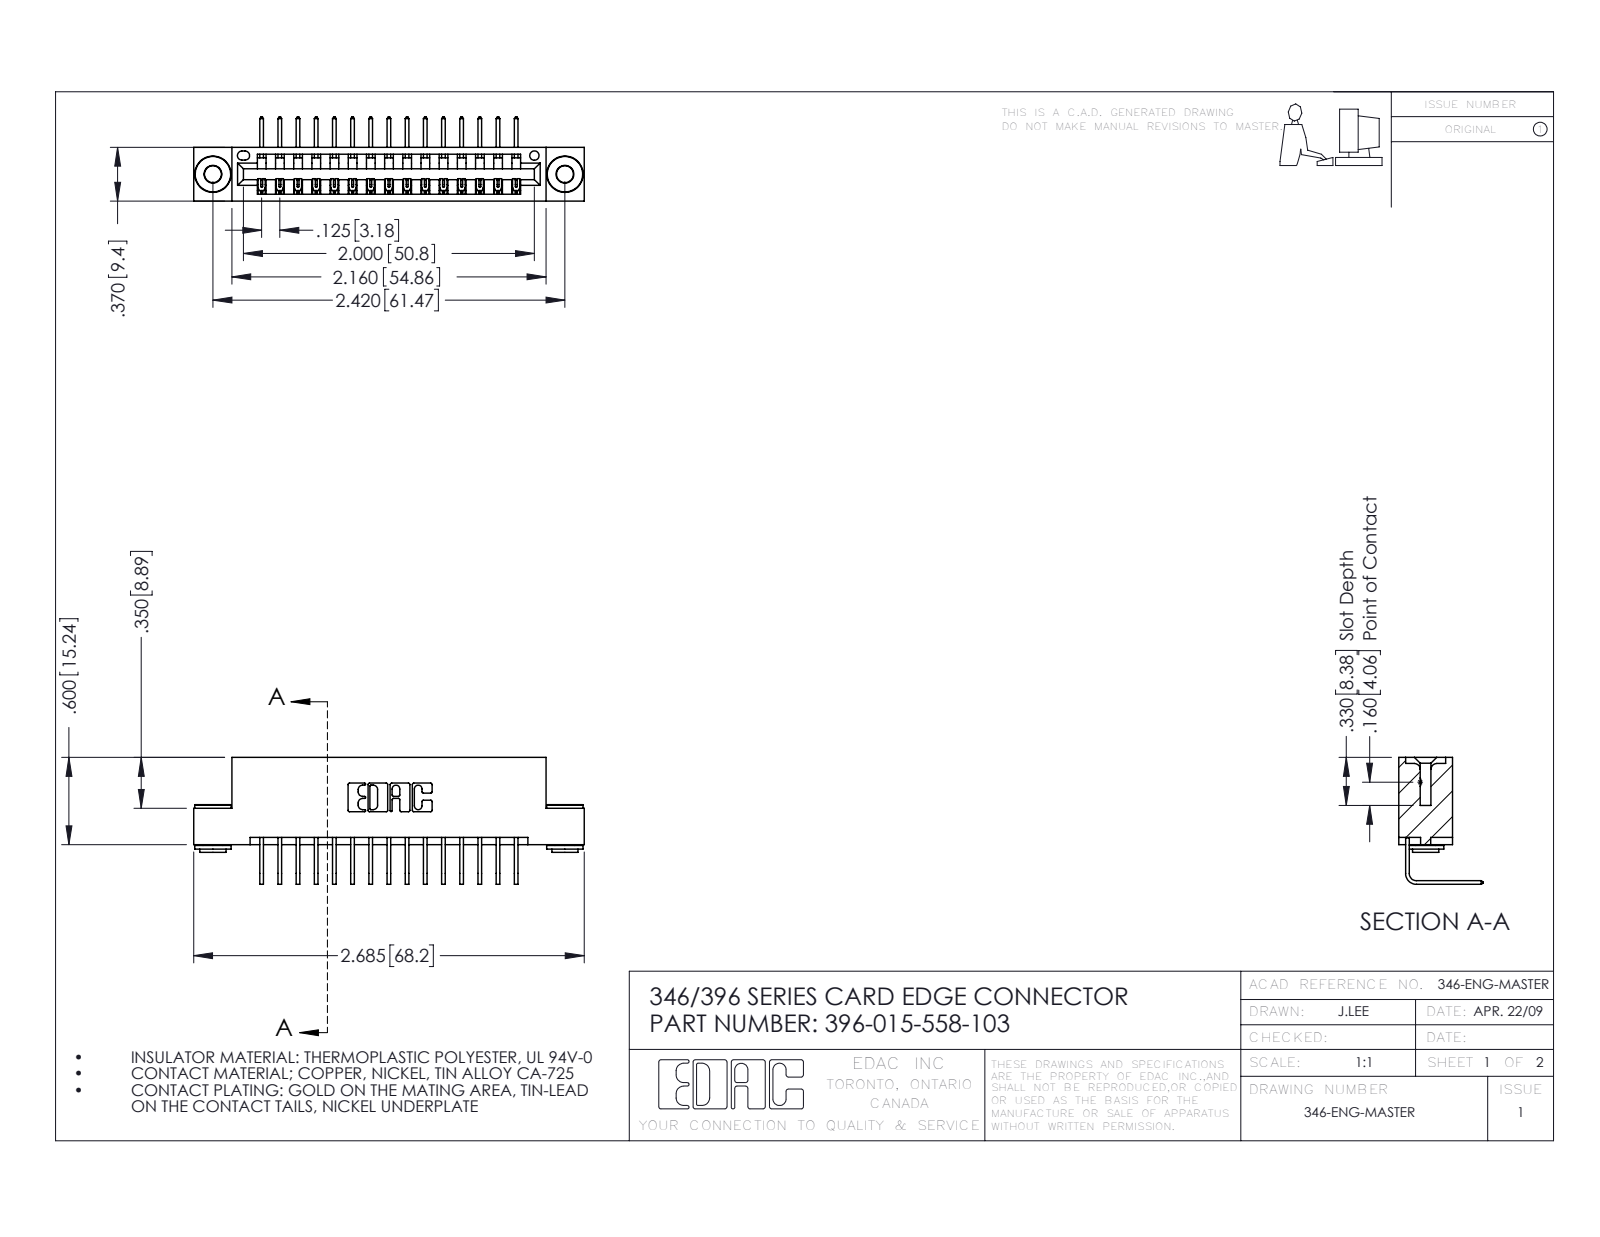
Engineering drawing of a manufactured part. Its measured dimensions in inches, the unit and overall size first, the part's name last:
Units: inches
Overall size (bounding box): 2.685 × 0.873 × 0.58
Round holes (diameter × count): ⌀0.116 ×2, ⌀0.156 ×2, ⌀0.064 ×1
Round bosses / shafts (diameter × count): ⌀0.25 ×2, ⌀0.18 ×2, ⌀0.136 ×2
Partial cylindrical surfaces — rounded edges, fillets, slot ends (radius × count): R0.006 ×30, R0.01 ×22, R0.007 ×6, R0.031 ×6, R0.026 ×3, R0.031 ×2, R0.04 ×2, R0.014 ×1
Main face-to-face distances: 0.322, 0.25, 0.048, 0.37, 0.025, 0.298, 0.072, 0.148, 0.222, 0.1
Hole centre spacings: 0.246, 2.213, 2.42
Volume: 0.391 in³ · Surface area: 12.77 in²
Bodies: 18 solids, 1060 faces (716 planar, 336 cylindrical, 8 other)
Part name (STEP PRODUCT): 396-015-558-103; 346 Part_Flush Mounting Lugs - 0.156 Dia-TH; 345-292-001_558 Tail - 2; 345-250-002_345-250-002-102
STEP written by: SolidWorks 2016 (CONFIG_CONTROL_DESIGN)
